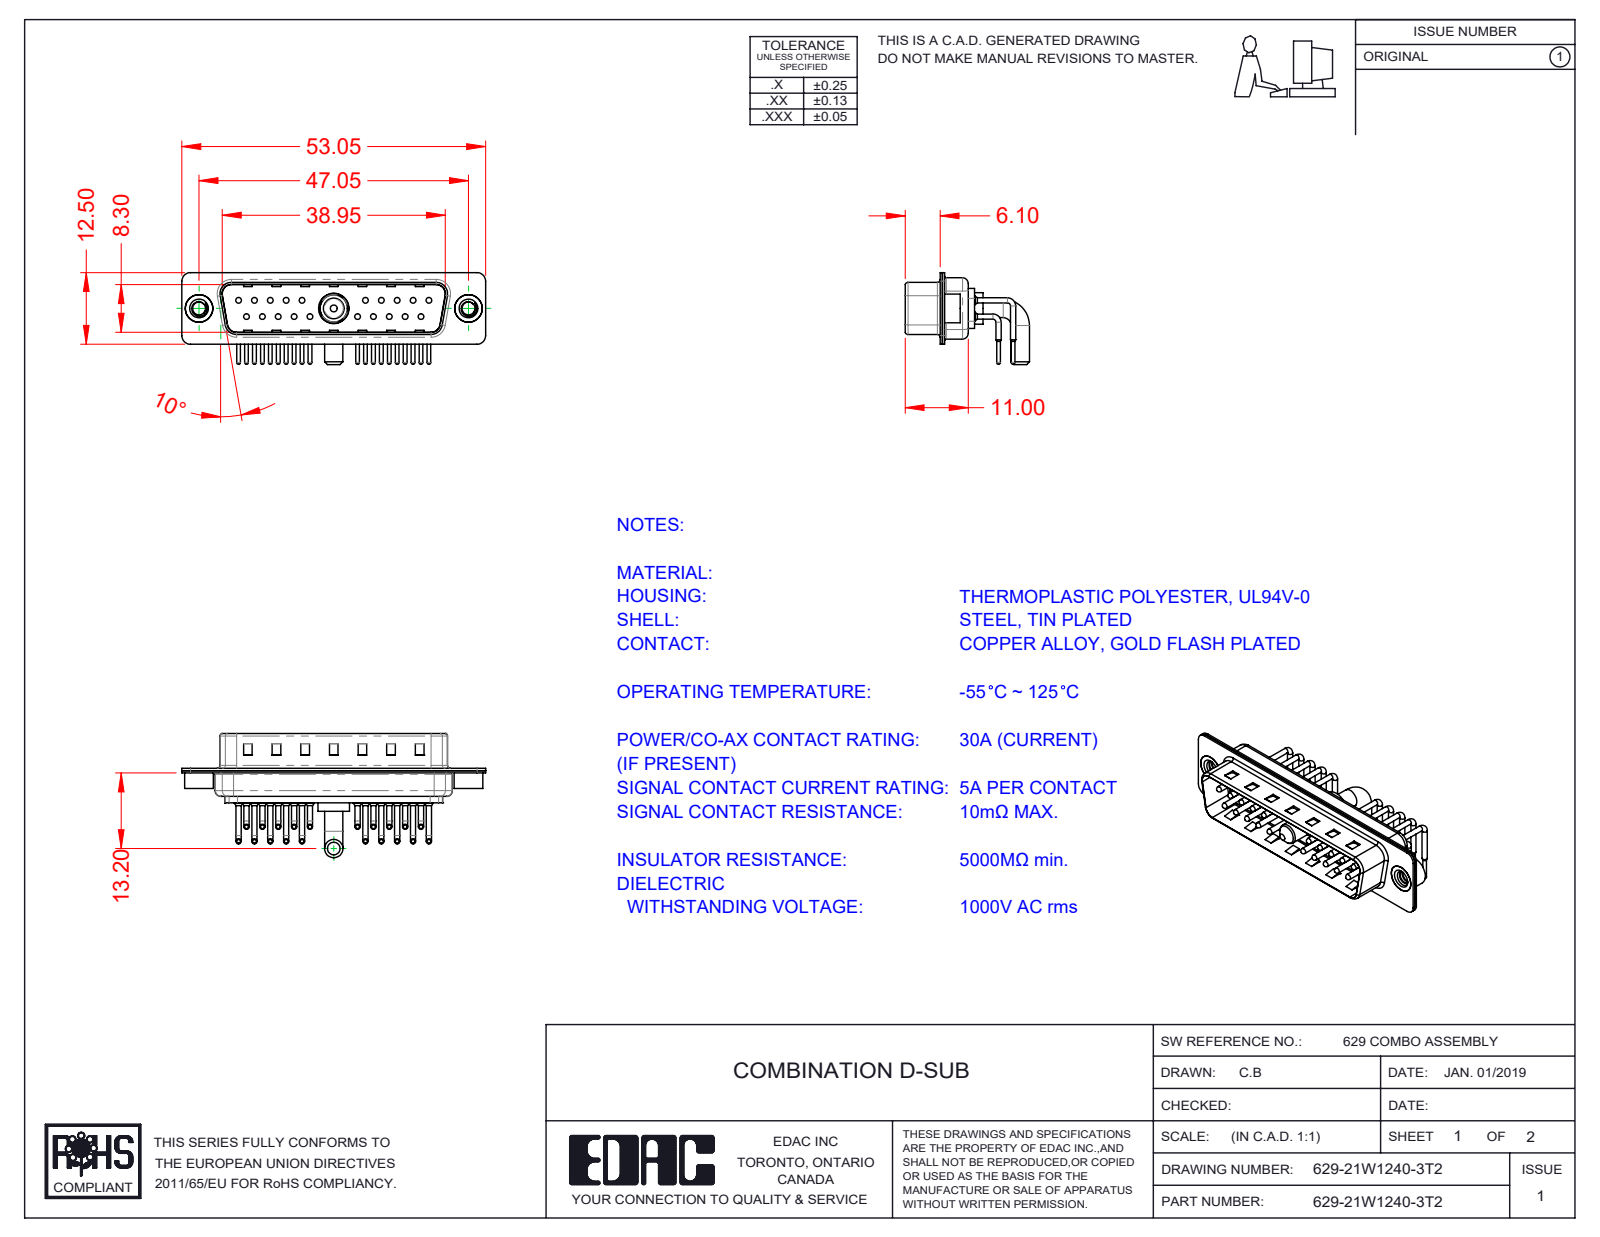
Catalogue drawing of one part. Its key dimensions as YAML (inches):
part_name: "Power Pin_30A RA; 629Combo Threaded Rivet_2; 629Combo Contact Row 2; 629Combo Shell Front_25 Contacts (+4 more)"
step_written_by: "SolidWorks 2020 (CONFIG_CONTROL_DESIGN)"
units: inches
bodies: {solids: 27, faces: 2619, planar: 1461, cylindrical: 878, other: 280}
overall_size: [2.089, 0.854, 0.632]
volume: 0.186
surface_area: 11.8
round_holes:
  - {diameter: 0.03, count: 20}
  - {diameter: 0.063, count: 20}
  - {diameter: 0.079, count: 20}
  - {diameter: 0.089, count: 2}
  - {diameter: 0.157, count: 2}
  - {diameter: 0.189, count: 2}
  - {diameter: 0.191, count: 1}
  - {diameter: 0.209, count: 1}
round_bosses_or_shafts:
  - {diameter: 0.035, count: 40}
  - {diameter: 0.059, count: 20}
  - {diameter: 0.039, count: 20}
  - {diameter: 0.026, count: 20}
  - {diameter: 0.197, count: 2}
  - {diameter: 0.193, count: 2}
  - {diameter: 0.126, count: 2}
  - {diameter: 0.217, count: 1}
partial_cylinders:
  - {radius: 0.04, count: 20}
  - {radius: 0.059, count: 16}
  - {radius: 0.079, count: 12}
  - {radius: 0.02, count: 8}
  - {radius: 0.063, count: 8}
  - {radius: 0.01, count: 4}
  - {radius: 0.024, count: 4}
  - {radius: 0.026, count: 4}
face_to_face_distances: [0.016, 0.031, 0.374, 0.358, 0.343, 0.39, 0.03, 0.047, 0.014, 0.22]
hole_center_spacings: [0.124, 0.109, 0.218, 0.327, 0.198, 0.763, 0.826, 0.872]
